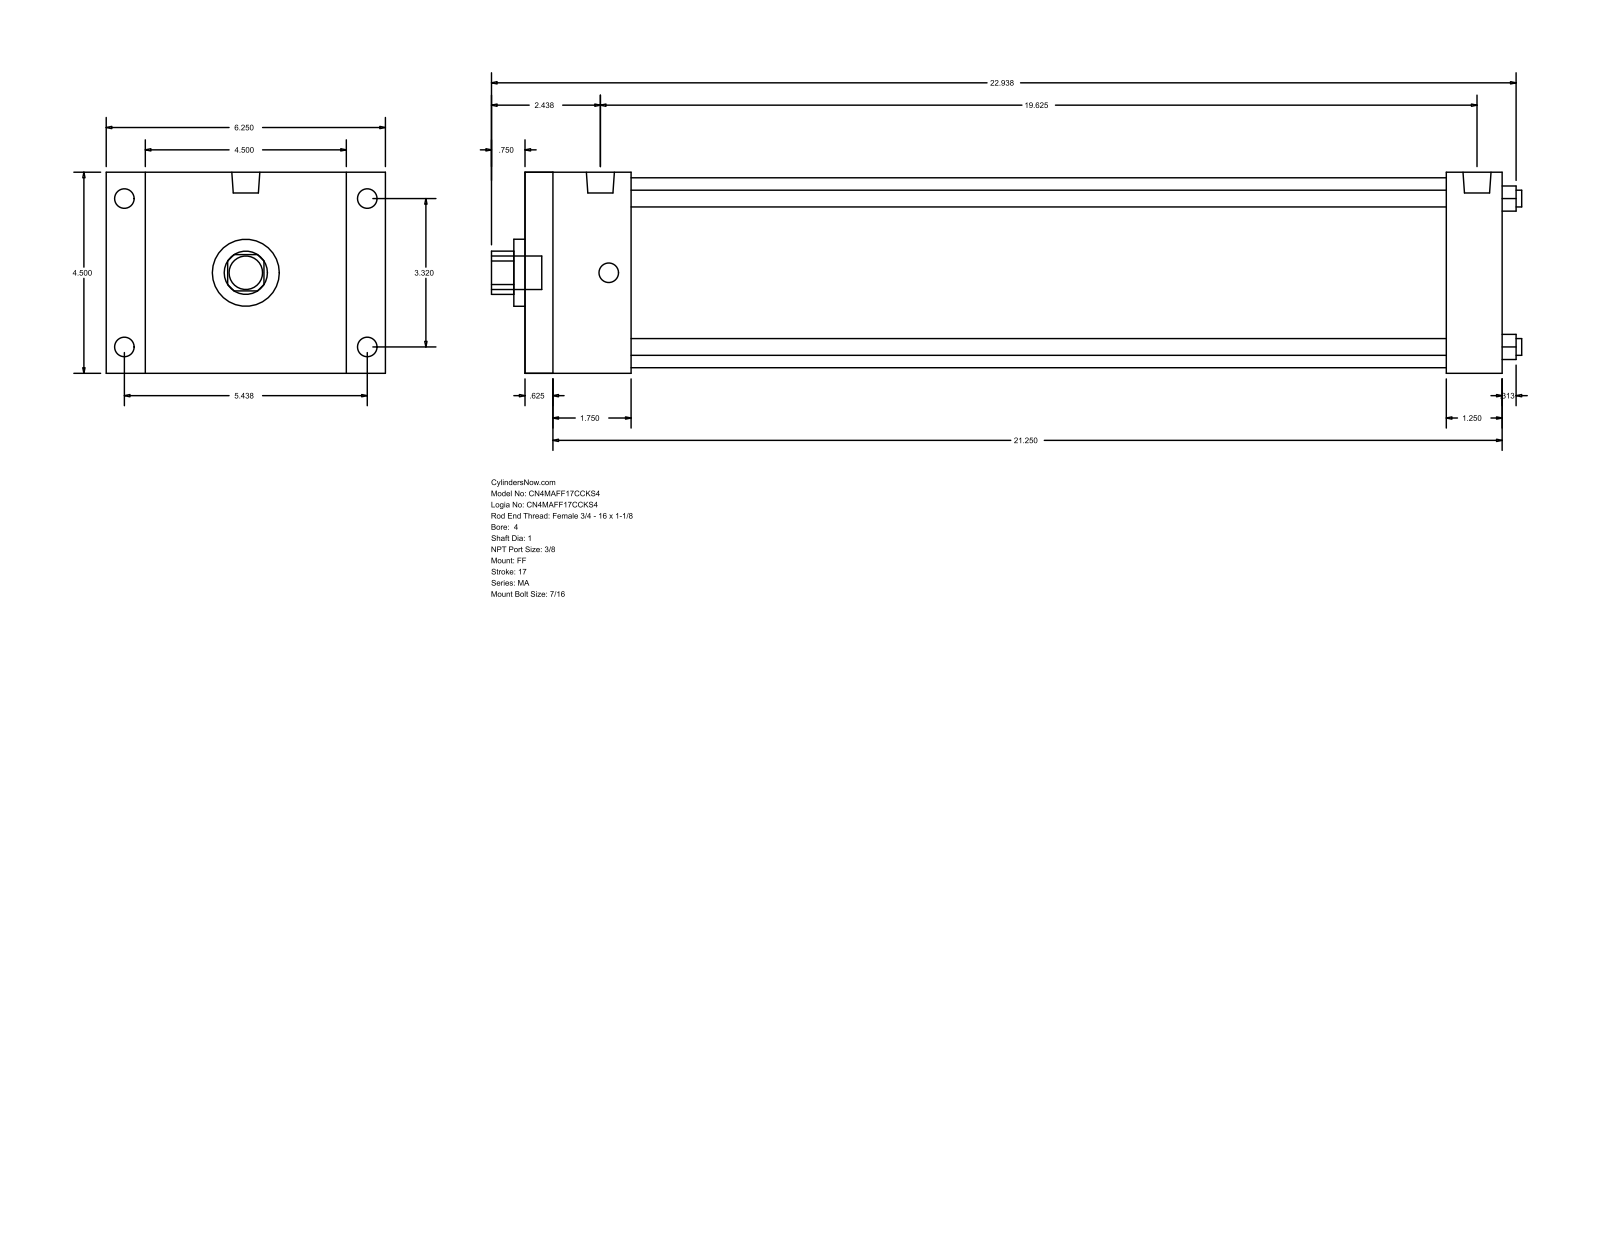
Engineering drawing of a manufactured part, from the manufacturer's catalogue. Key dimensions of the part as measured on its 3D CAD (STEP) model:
Part name (STEP PRODUCT): MA_FF__0400_1
STEP written by: GSSL Pune (CONFIG_CONTROL_DESIGN)
Units: millimetres
Bodies: 0 solids, 92 faces (64 planar, 28 cylindrical, 0 other)
Overall size (bounding box): 585.79 × 158.75 × 114.3
Round holes (diameter × count): ⌀9.53 ×4, ⌀25.4 ×1, ⌀38.1 ×1, ⌀107.95 ×1
Round bosses / shafts (diameter × count): ⌀11.11 ×8, ⌀15.93 ×2, ⌀19.05 ×1
Partial cylindrical surfaces — rounded edges, fillets, slot ends (radius × count): R12.29 ×1
Main face-to-face distances: 114.3, 555.62, 15.87, 539.75, 22.23, 136.53, 523.87, 508, 31.75, 60.33
Hole centre spacings: 59.62, 84.32, 119.25
